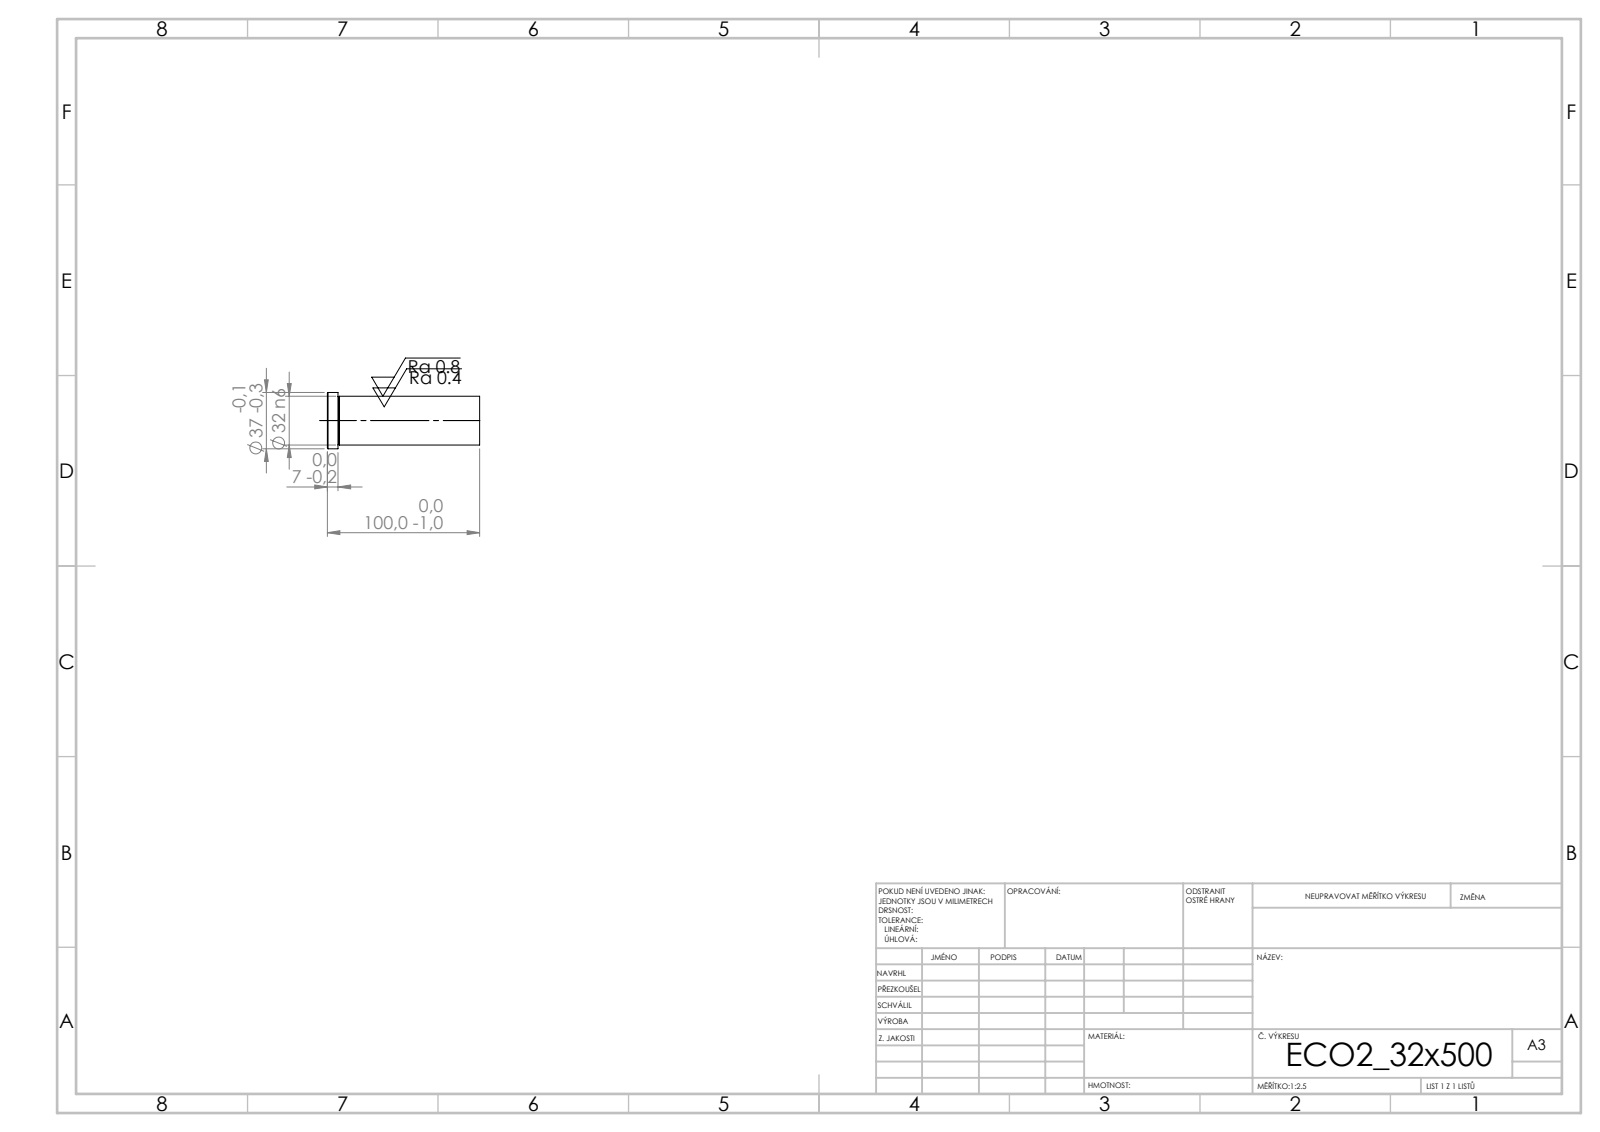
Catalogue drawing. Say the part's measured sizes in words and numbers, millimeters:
Its 3-D file was written by "SolidWorks 2019 (CONFIG_CONTROL_DESIGN)". It is 1 solid with 13 faces: 3 planar, 4 cylindrical and 6 other. Overall it measures 100 by 37 by 37 millimeters. Its volume is 82 268 cubic millimeters and its surface area 12 333 square millimeters. Round bosses or shafts: 1 of diameter 37, 1 of diameter 32. The main face-to-face distances are 100, 93, 7.
